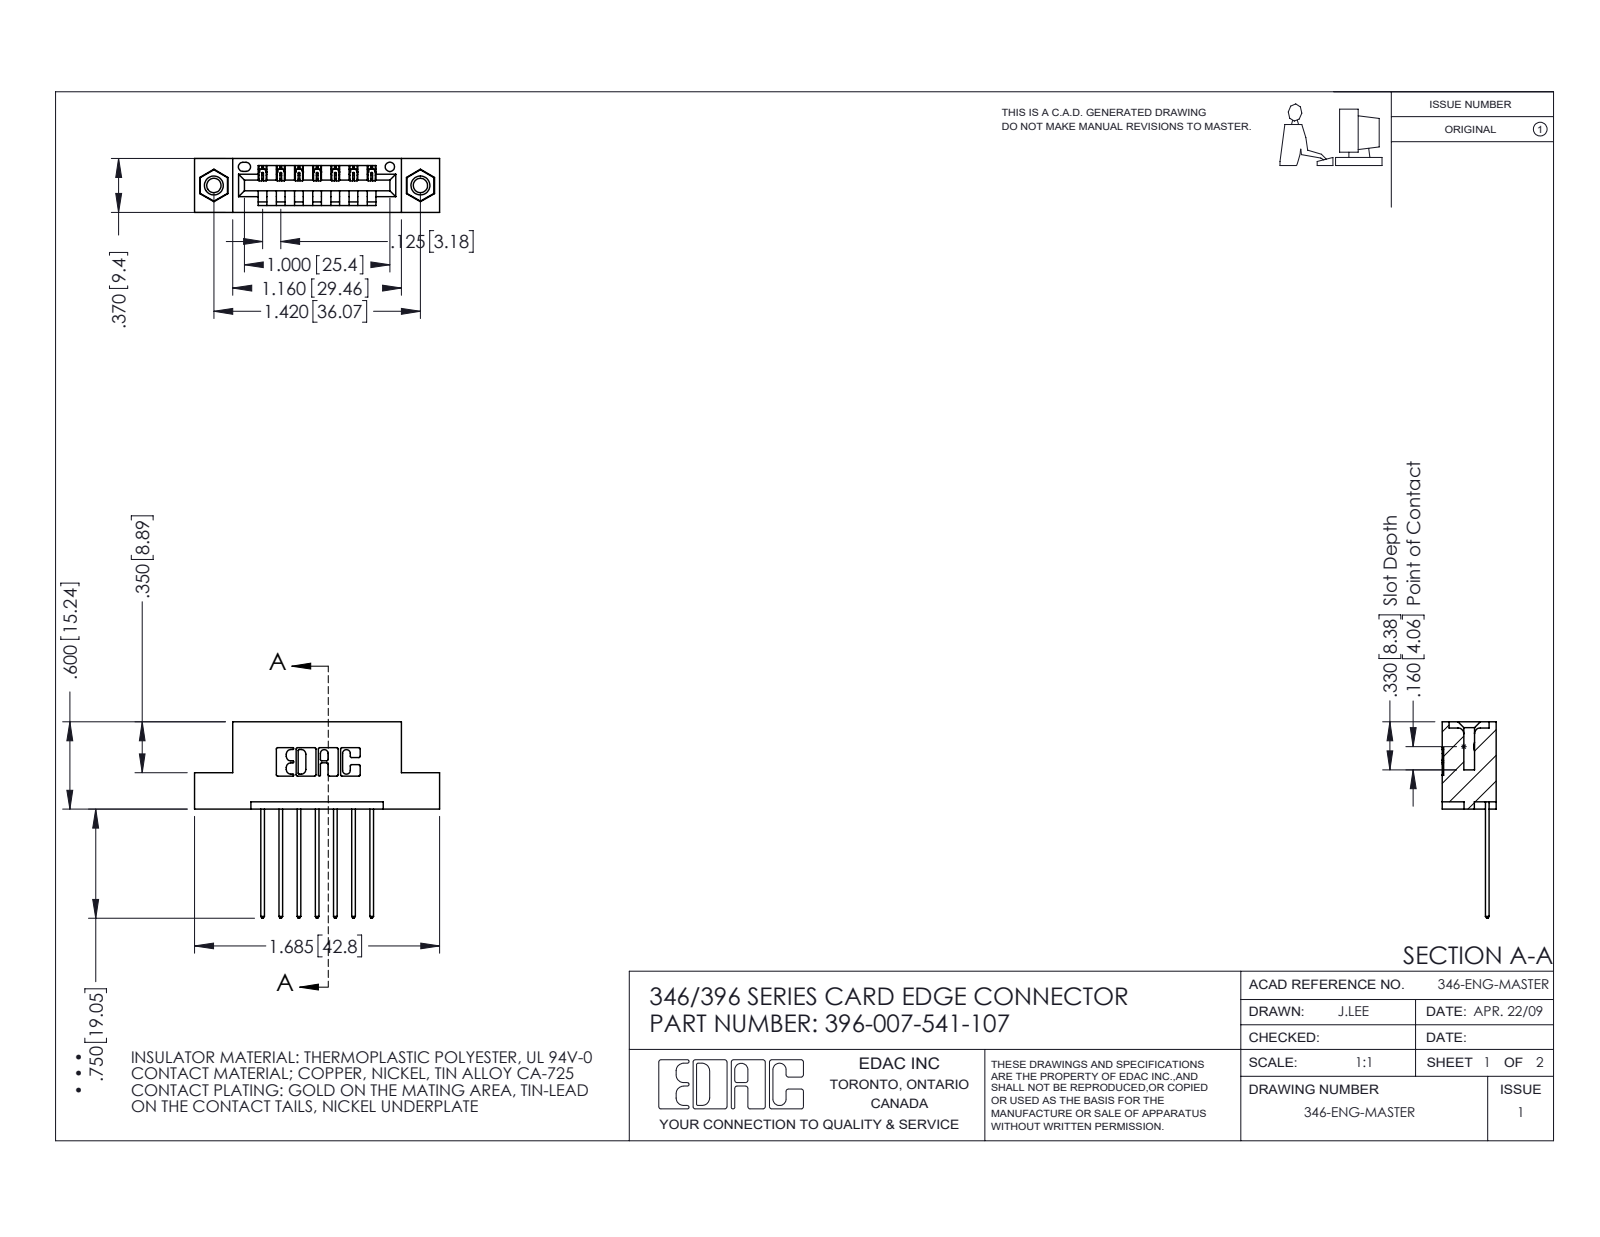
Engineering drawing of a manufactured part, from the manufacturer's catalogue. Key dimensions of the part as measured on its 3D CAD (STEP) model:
Part name (STEP PRODUCT): 396-007-541-107; 345-250-001_345-250-005-103; 346 Part_Flush Mounting Lugs - 0.156 Dia-TI; 345-292-001_345-293-141
STEP written by: SolidWorks 2016 (CONFIG_CONTROL_DESIGN)
Units: inches
Bodies: 10 solids, 588 faces (388 planar, 184 cylindrical, 16 other)
Overall size (bounding box): 1.685 × 1.35 × 0.37
Volume: 0.236 in³ · Surface area: 7.17 in²
Round holes (diameter × count): ⌀0.098 ×2, ⌀0.125 ×2, ⌀0.156 ×2, ⌀0.064 ×1
Round bosses / shafts (diameter × count): ⌀0.155 ×2
Partial cylindrical surfaces — rounded edges, fillets, slot ends (radius × count): R0.01 ×22, R0.006 ×14, R0.01 ×14, R0.007 ×6, R0.031 ×6, R0.026 ×3, R0.031 ×2, R0.04 ×2
Main face-to-face distances: 0.25, 0.048, 0.322, 0.37, 0.072, 0.298, 0.025, 0.148, 0.222, 0.1
Hole centre spacings: 0.246, 1.217, 1.42
